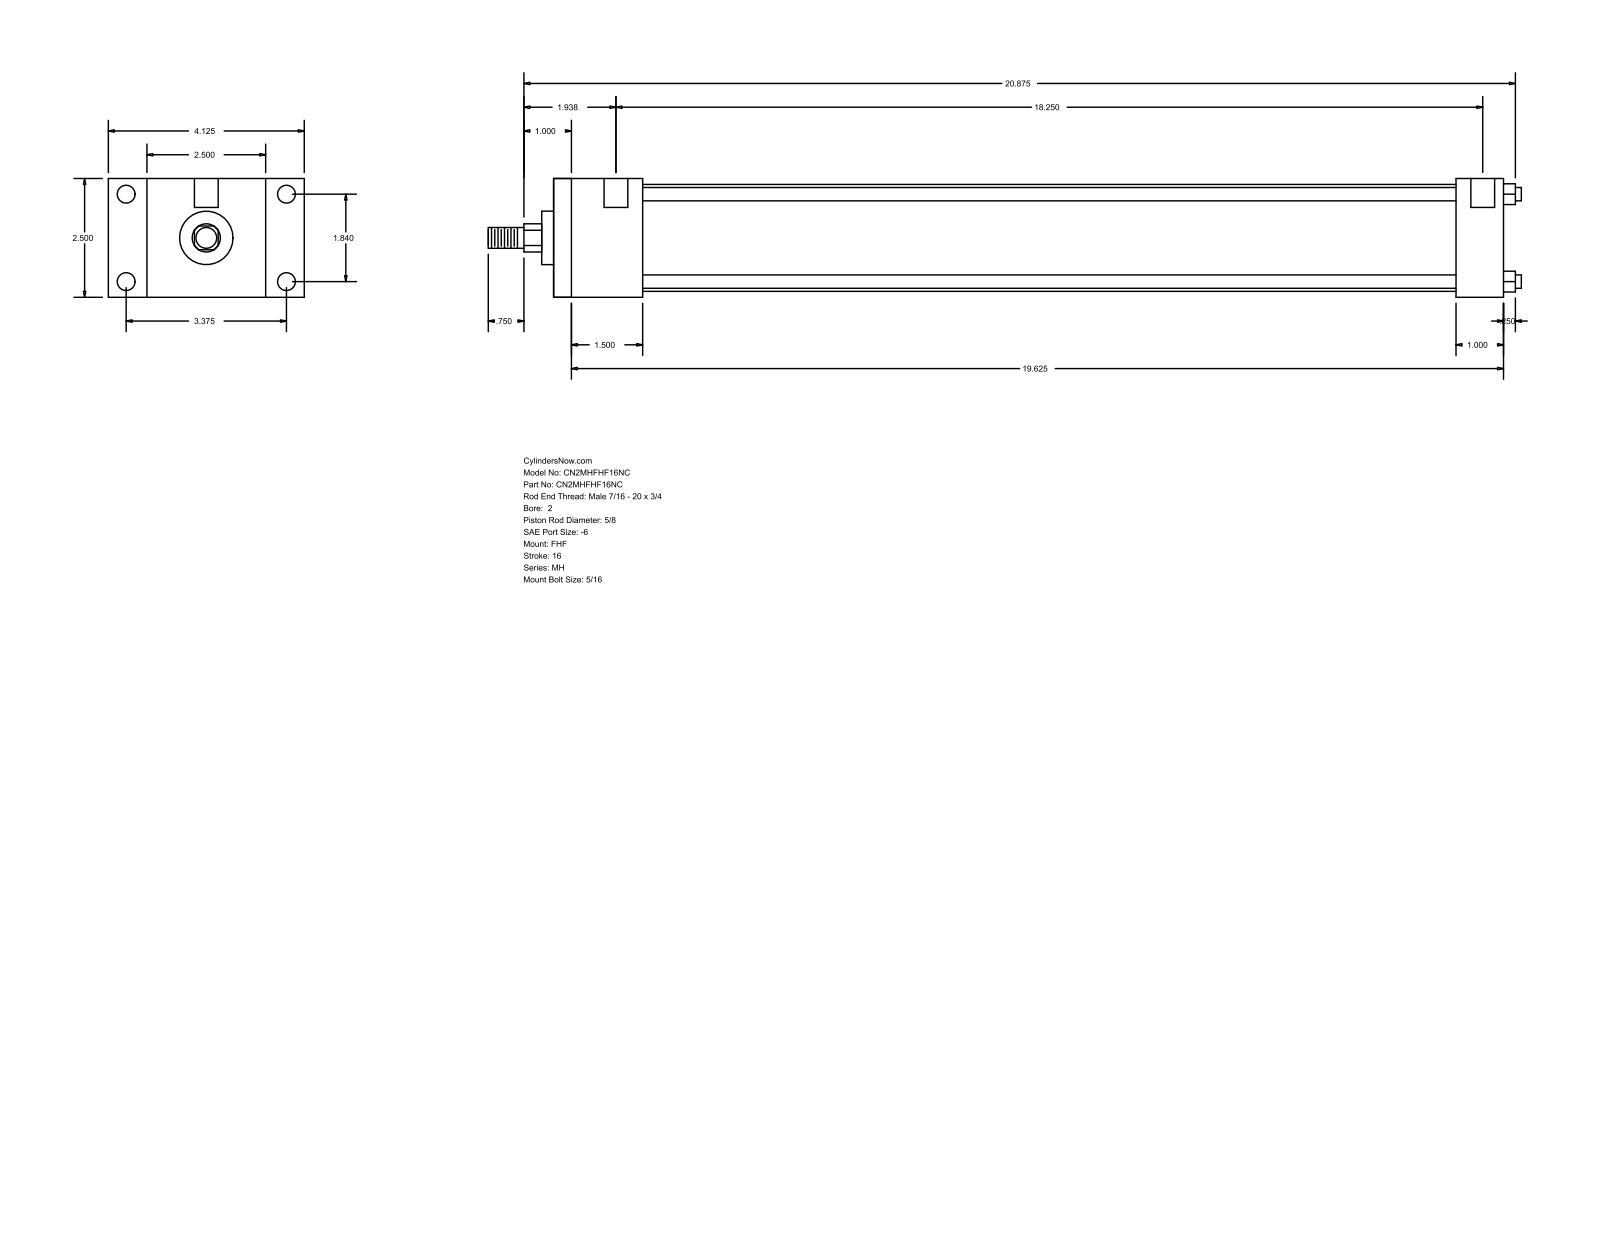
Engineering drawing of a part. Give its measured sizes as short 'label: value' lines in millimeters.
name: MH_FHF__0200_0.625
written by: GSSL Pune (CONFIG_CONTROL_DESIGN)
unit: mm
bodies: 0 solids, 88 faces (60 planar, 28 cylindrical, 0 other)
size: 552.45 × 104.78 × 63.5
holes: 4× ⌀5.56, 4× ⌀9.53, 2× ⌀12.7
bosses: 4× ⌀7.14, 1× ⌀57.15, 1× ⌀28.57, 1× ⌀15.88, 1× ⌀11.11
rounds: 1× R7.54
face distances: 63.5, 47.62, 508, 460.38, 20.64, 84.14, 104.78, 25.4, 482.6, 434.98
hole spacings: 46.74, 85.72, 97.63, 471.49, 3.18, 4.76, 463.55, 466.73
